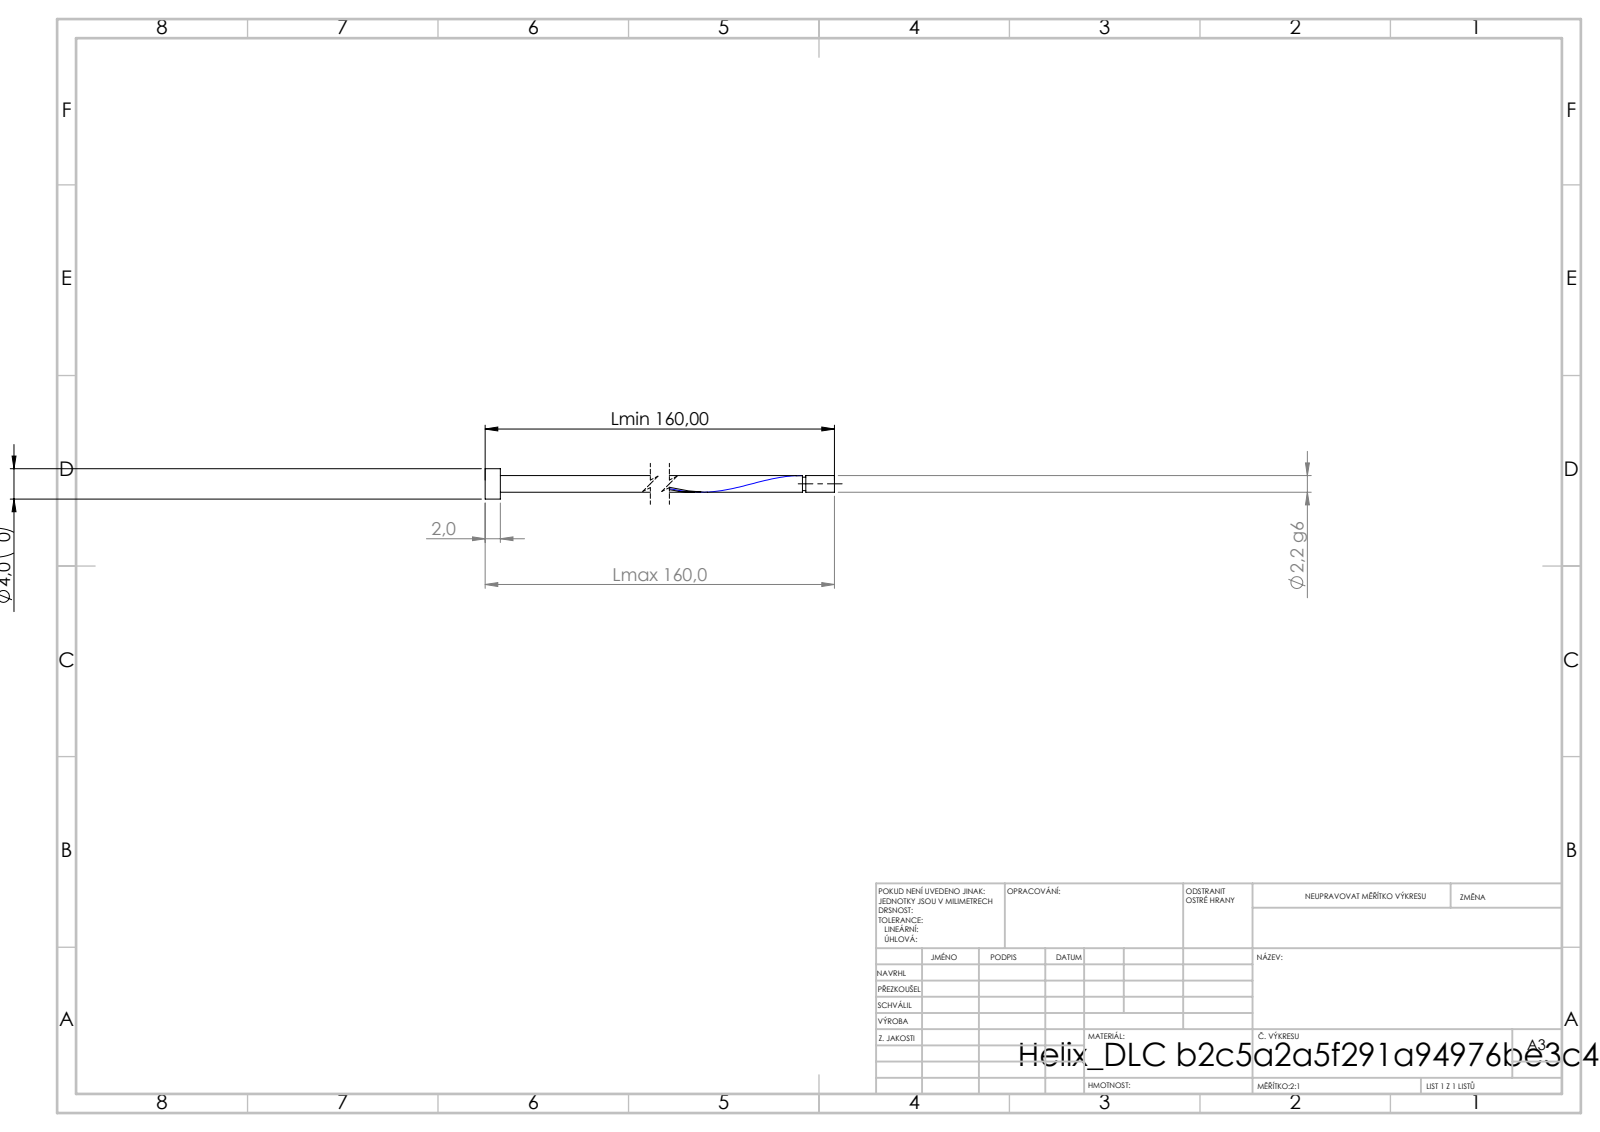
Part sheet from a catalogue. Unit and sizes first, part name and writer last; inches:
Units: inches
Overall size (bounding box): 6.299 × 0.157 × 0.157
Round bosses / shafts (diameter × count): ⌀0.157 ×1, ⌀0.087 ×1, ⌀0.069 ×1
Main face-to-face distances: 0.079, 6.299, 6.22, 6.151, 6.072, 0.148, 6.133, 6.055, 0.017, 0.166
Volume: 0.046 in³ · Surface area: 2.372 in²
Bodies: 1 solid, 16 faces (6 planar, 9 cylindrical, 1 other)
STEP written by: SolidWorks 2019 (CONFIG_CONTROL_DESIGN)
